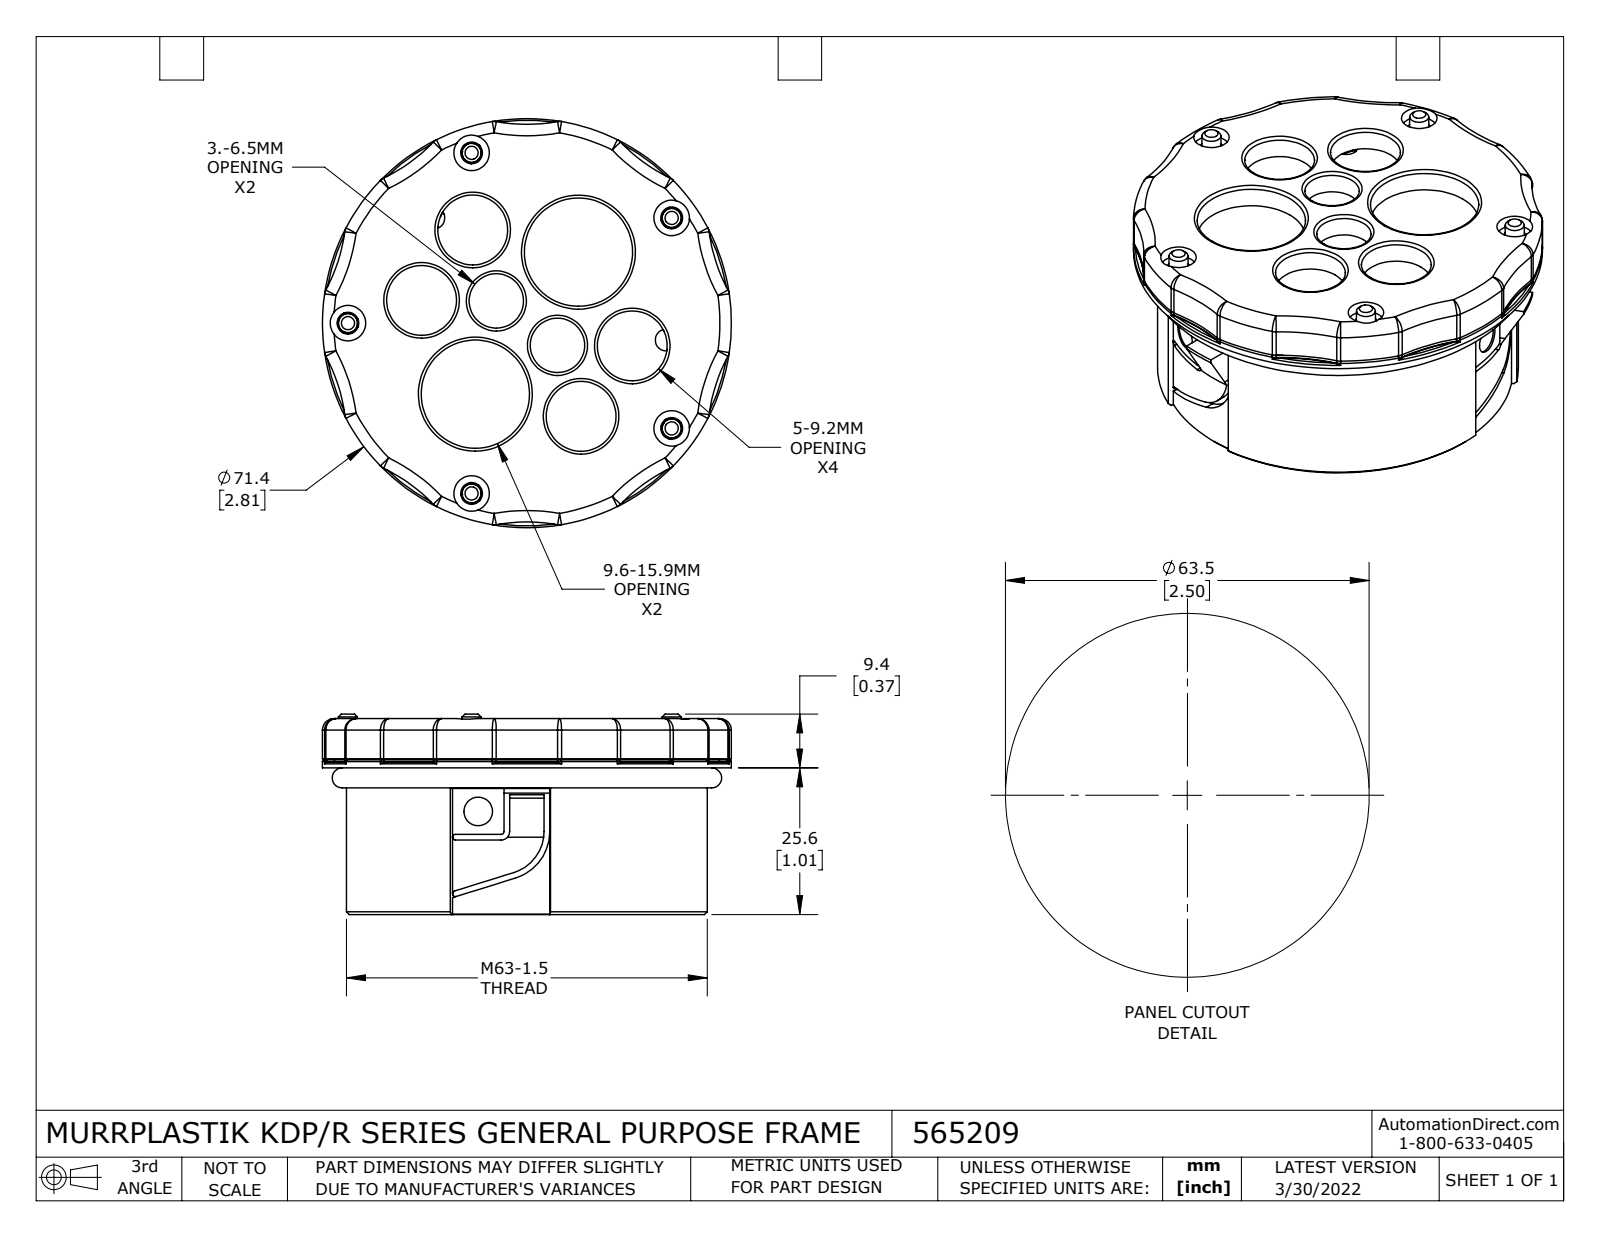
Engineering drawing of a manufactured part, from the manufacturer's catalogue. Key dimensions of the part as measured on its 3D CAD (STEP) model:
Part name (STEP PRODUCT): 565209
STEP written by: SolidWorks 2021 (CONFIG_CONTROL_DESIGN)
Units: millimetres
Bodies: 6 solids, 557 faces (89 planar, 243 cylindrical, 225 other)
Overall size (bounding box): 71.4 × 71.4 × 35
Volume: 44 348 mm³ · Surface area: 44 069 mm²
Round holes (diameter × count): ⌀3.8 ×8, ⌀6.2 ×5, ⌀12.2 ×4, ⌀5 ×3, ⌀9.5 ×2, ⌀18.9 ×2, ⌀4 ×1, ⌀54.9 ×1, ⌀58 ×1, ⌀67.4 ×1
Round bosses / shafts (diameter × count): ⌀71.4 ×1, ⌀66.4 ×1, ⌀64 ×1, ⌀63 ×1, ⌀61.7 ×1, ⌀59 ×1, ⌀55.7 ×1, ⌀51.71 ×1
Partial cylindrical surfaces — rounded edges, fillets, slot ends (radius × count): R2 ×22, R30 ×10, R0.5 ×9, R0.3 ×6, R1.5 ×3, R7.5 ×3, R8.5 ×3, R2.4 ×2
Main face-to-face distances: 1.75, 3.5, 4, 7.5, 5.75, 4.7, 8.2, 6.45, 12.2, 1.6
Hole centre spacings: 31.25, 59.44, 13.05, 16.68, 18.81, 18.86, 24.99, 28.65
